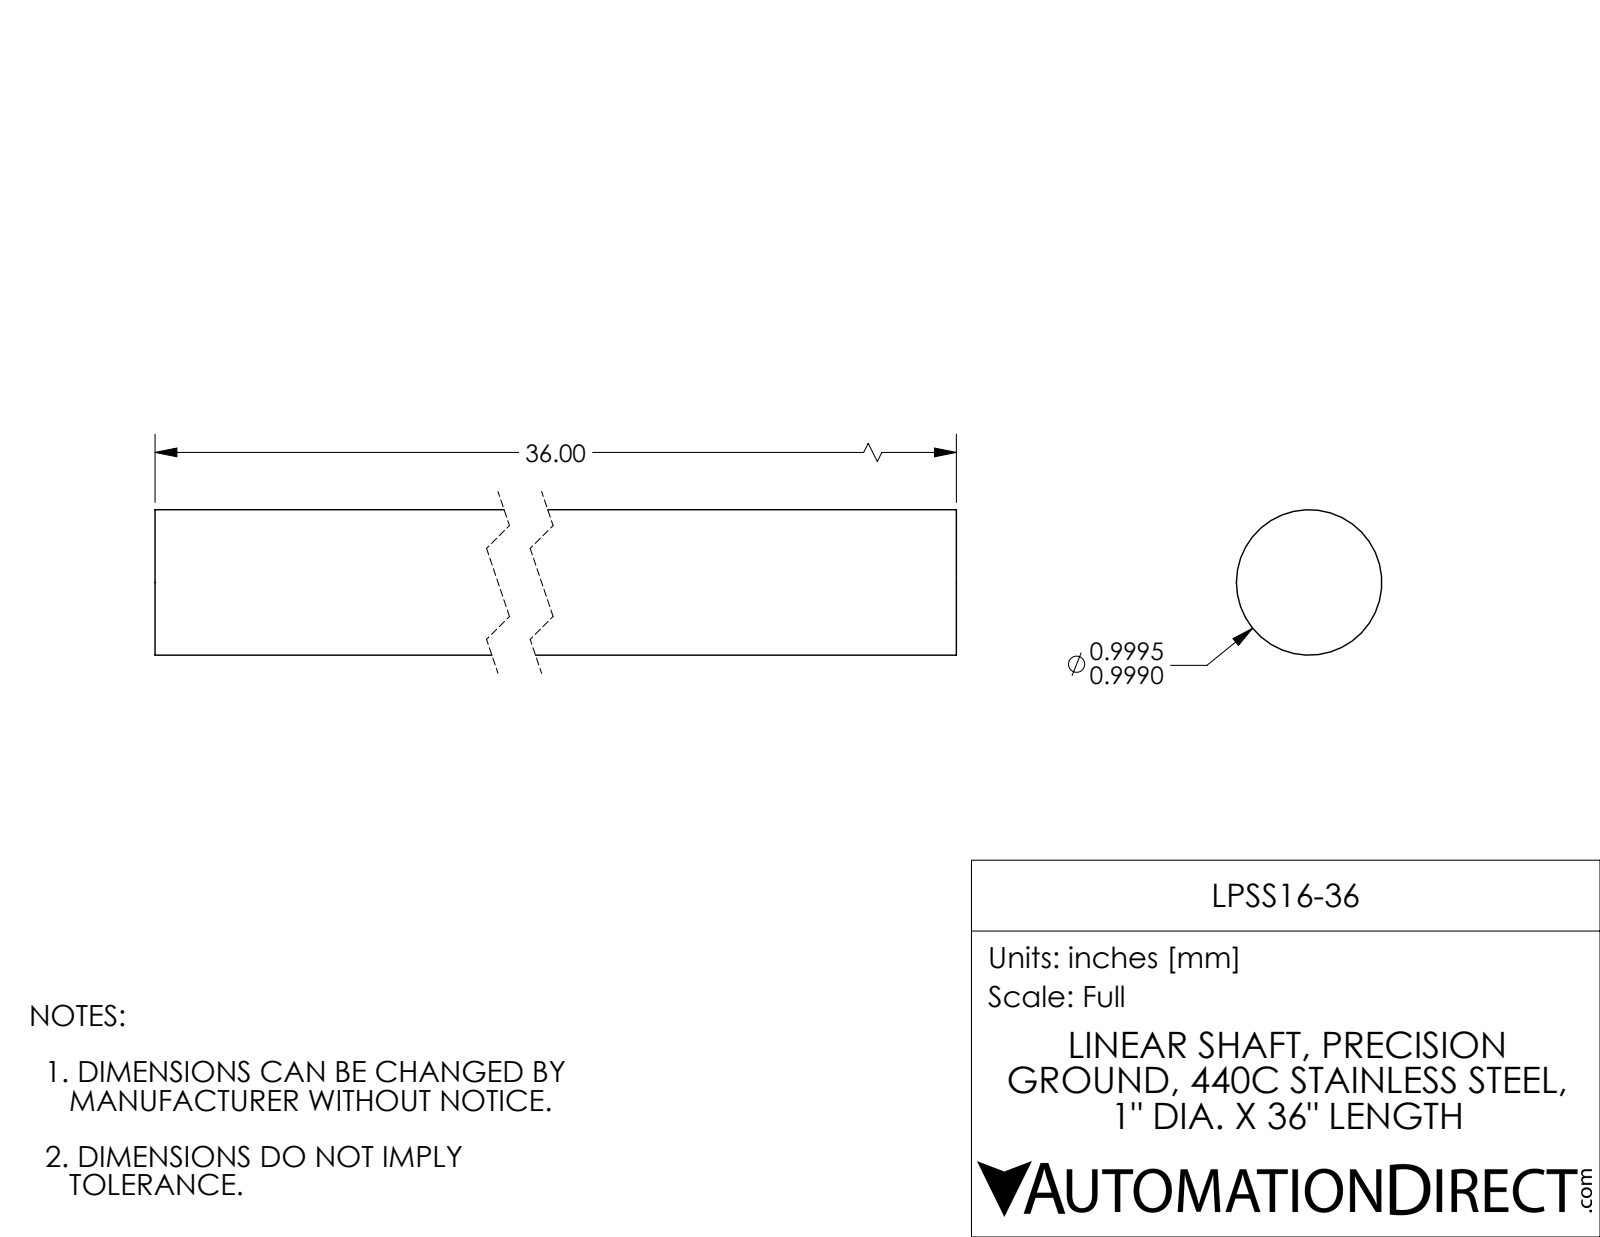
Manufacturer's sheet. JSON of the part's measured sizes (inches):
{"part_name": "LPSS16-36", "step_written_by": "SolidWorks 2017 (AUTOMOTIVE_DESIGN)", "units": "inches", "bodies": {"solids": 1, "faces": 4, "planar": 2, "cylindrical": 2, "other": 0}, "overall_size": [36, 0.999, 0.999], "volume_in3": 28.25, "surface_area_in2": 114.6, "round_bosses_or_shafts": [[1, 1]], "face_to_face_distances": [36]}
